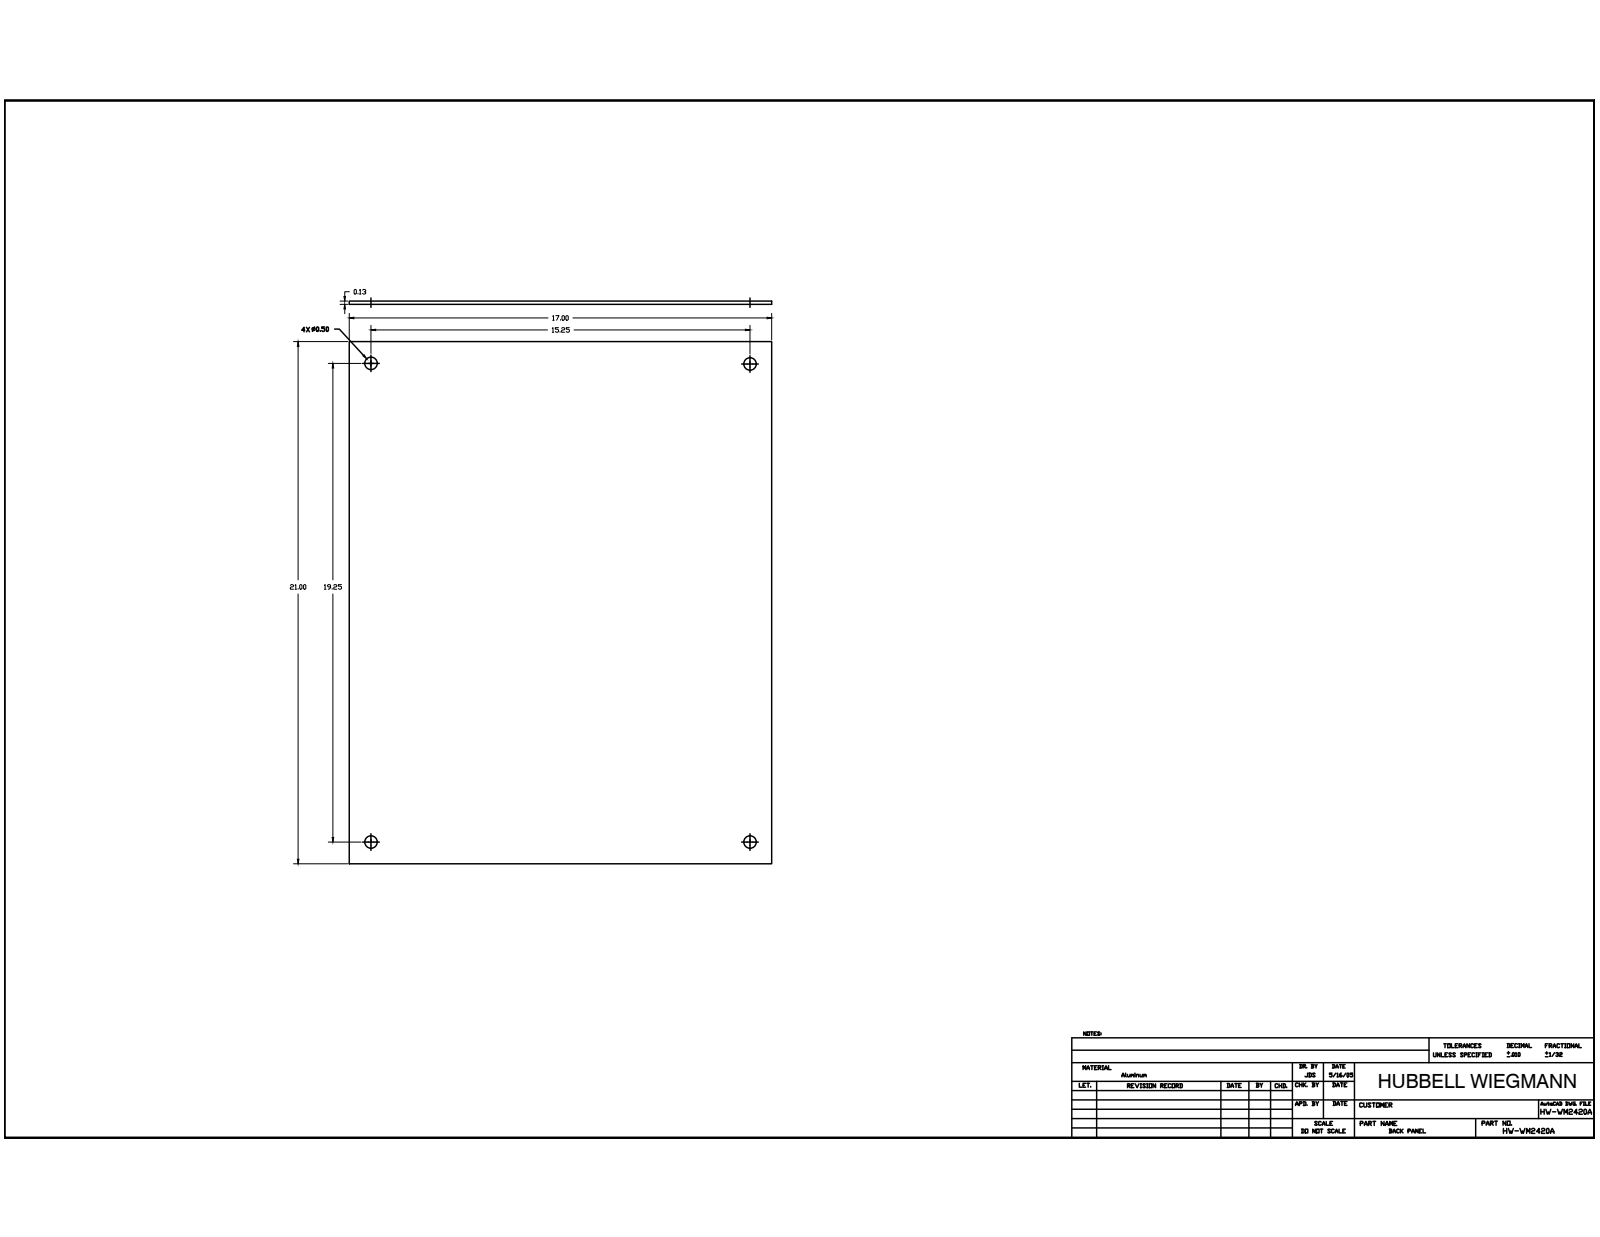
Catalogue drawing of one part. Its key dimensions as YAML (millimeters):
part_name: "BP2420AL_STP"
step_written_by: "Autodesk Inventor 2014 (AUTOMOTIVE_DESIGN)"
units: millimeters
bodies: {solids: 1, faces: 10, planar: 6, cylindrical: 4, other: 0}
overall_size: [533.4, 431.8, 3.3]
volume: 758850
surface_area: 466532
round_holes:
  - {diameter: 12.7, count: 4}
face_to_face_distances: [3.3, 431.8, 533.4]
hole_center_spacings: [387.34, 488.95, 623.78]
